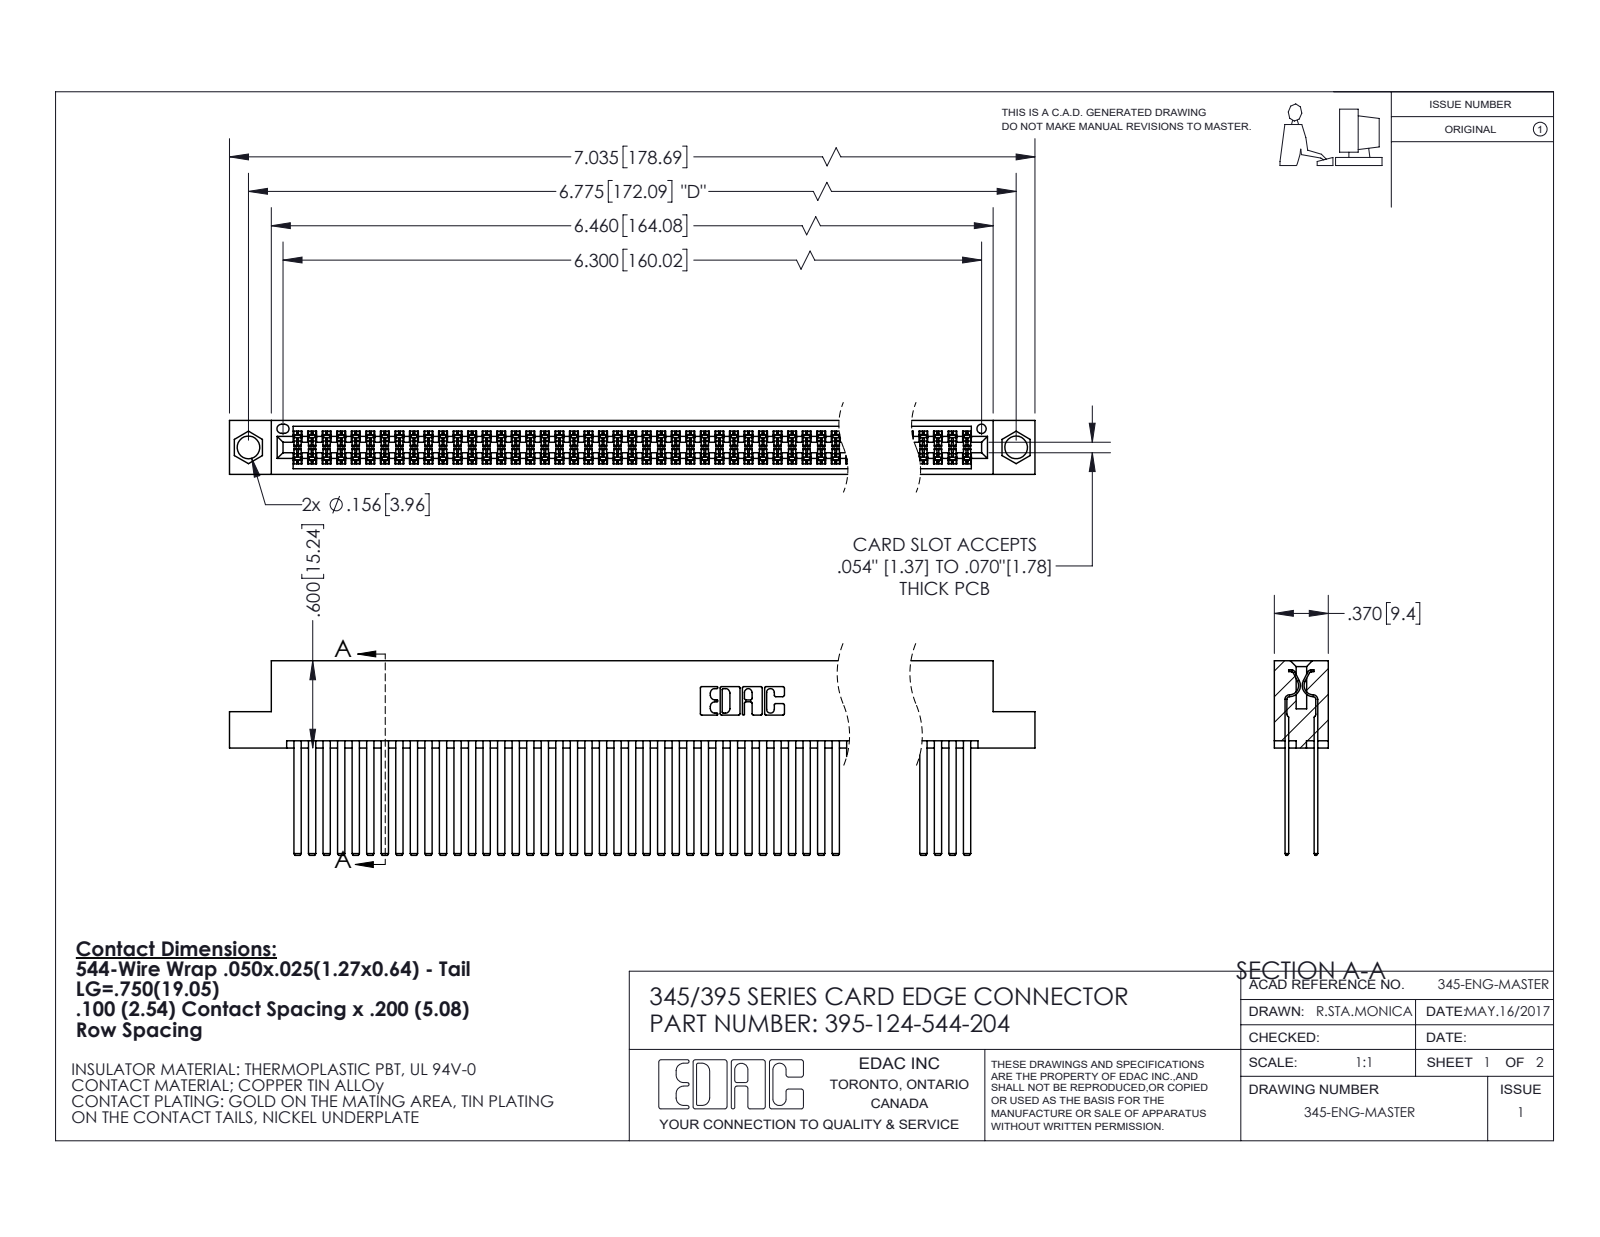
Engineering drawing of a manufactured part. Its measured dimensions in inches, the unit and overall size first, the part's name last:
Units: inches
Overall size (bounding box): 7.035 × 1.337 × 0.37
Round holes (diameter × count): ⌀0.156 ×2, ⌀0.064 ×1
Partial cylindrical surfaces — rounded edges, fillets, slot ends (radius × count): R0.006 ×186, R0.01 ×22, R0.007 ×6, R0.031 ×6, R0.026 ×3, R0.014 ×2, R0.019 ×2, R0.022 ×2
Main face-to-face distances: 0.2, 0.025, 0.298, 0.072, 0.098, 0.272, 0.225, 0.175, 0.37, 0.05
Hole centre spacings: 0.27, 6.539, 6.775
Volume: 1.17 in³ · Surface area: 52.2 in²
Bodies: 125 solids, 5596 faces (3690 planar, 1906 cylindrical, 0 other)
Part name (STEP PRODUCT): 395-124-544-204; 345-292-001_345-293-144; 345 Part_Flush Mounting Lugs - 0.156 Dia-TI
STEP written by: SolidWorks 2020 (CONFIG_CONTROL_DESIGN)
